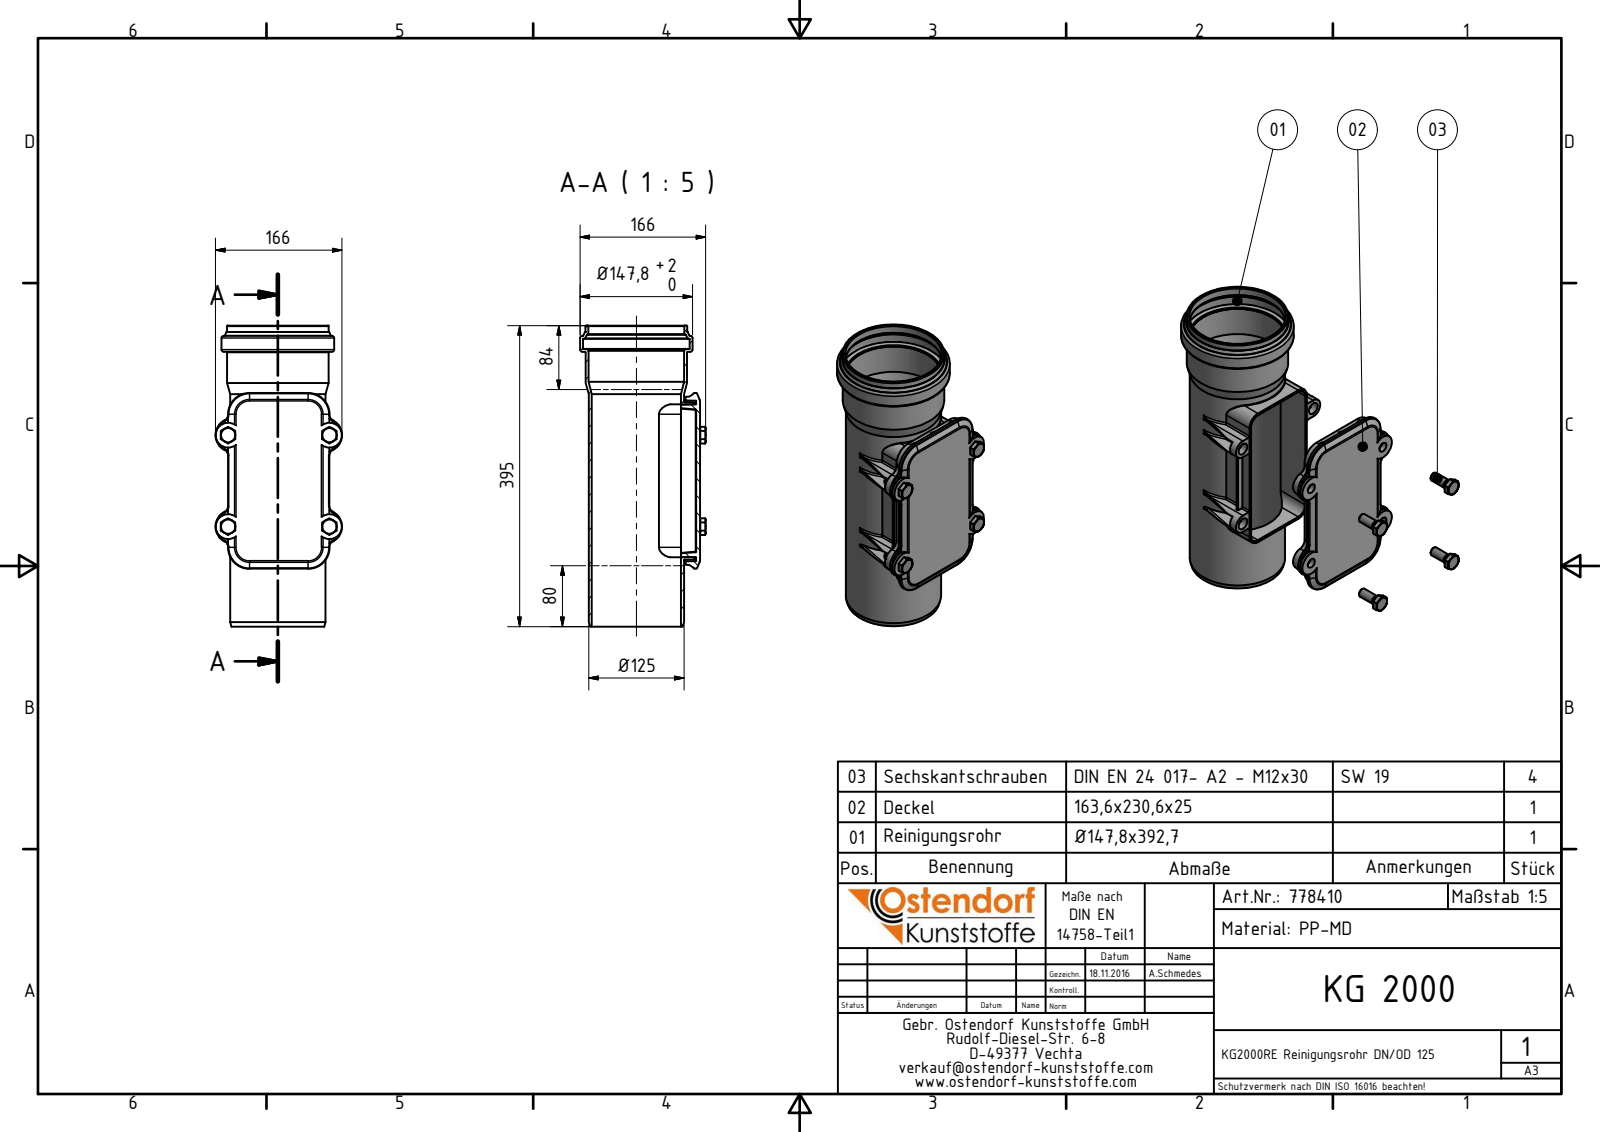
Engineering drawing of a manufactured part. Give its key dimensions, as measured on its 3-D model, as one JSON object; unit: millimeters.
{"part_name": "778410 KG2000RE Reinigungsrohr DN_OD 125; 778410 KG2000RE Reinigungsrohr DN_OD 125 Deckel; DIN 933 - M12 x 30; 778410 KG2000RE Reinigungsrohr DN_OD 125 Zusammenbau", "step_written_by": "Autodesk Inventor 2016 (AUTOMOTIVE_DESIGN)", "units": "millimeters", "bodies": {"solids": 6, "faces": 673, "planar": 224, "cylindrical": 198, "other": 251}, "overall_size": [395, 166, 164.9], "volume_mm3": 958398, "surface_area_mm2": 463424, "round_holes": [[13, 4], [16, 4], [116.9, 1], [125.6, 1], [125.9, 1], [140.2, 1]], "round_bosses_or_shafts": [[17.2, 4], [12, 4], [11.05, 4], [147.8, 1], [133.5, 1], [133.2, 1], [125.1, 1]], "partial_cylinders_radius": [[0.5, 44], [2, 20], [1, 16], [5, 12], [8, 8], [13, 8], [1.5, 4], [16, 4]], "face_to_face_distances": [3, 5, 103.6, 100.6, 38, 29.38, 67.38, 8, 20, 19], "hole_center_spacings": [120, 2.4, 120.02, 130.6, 133, 177.36, 179.13]}
